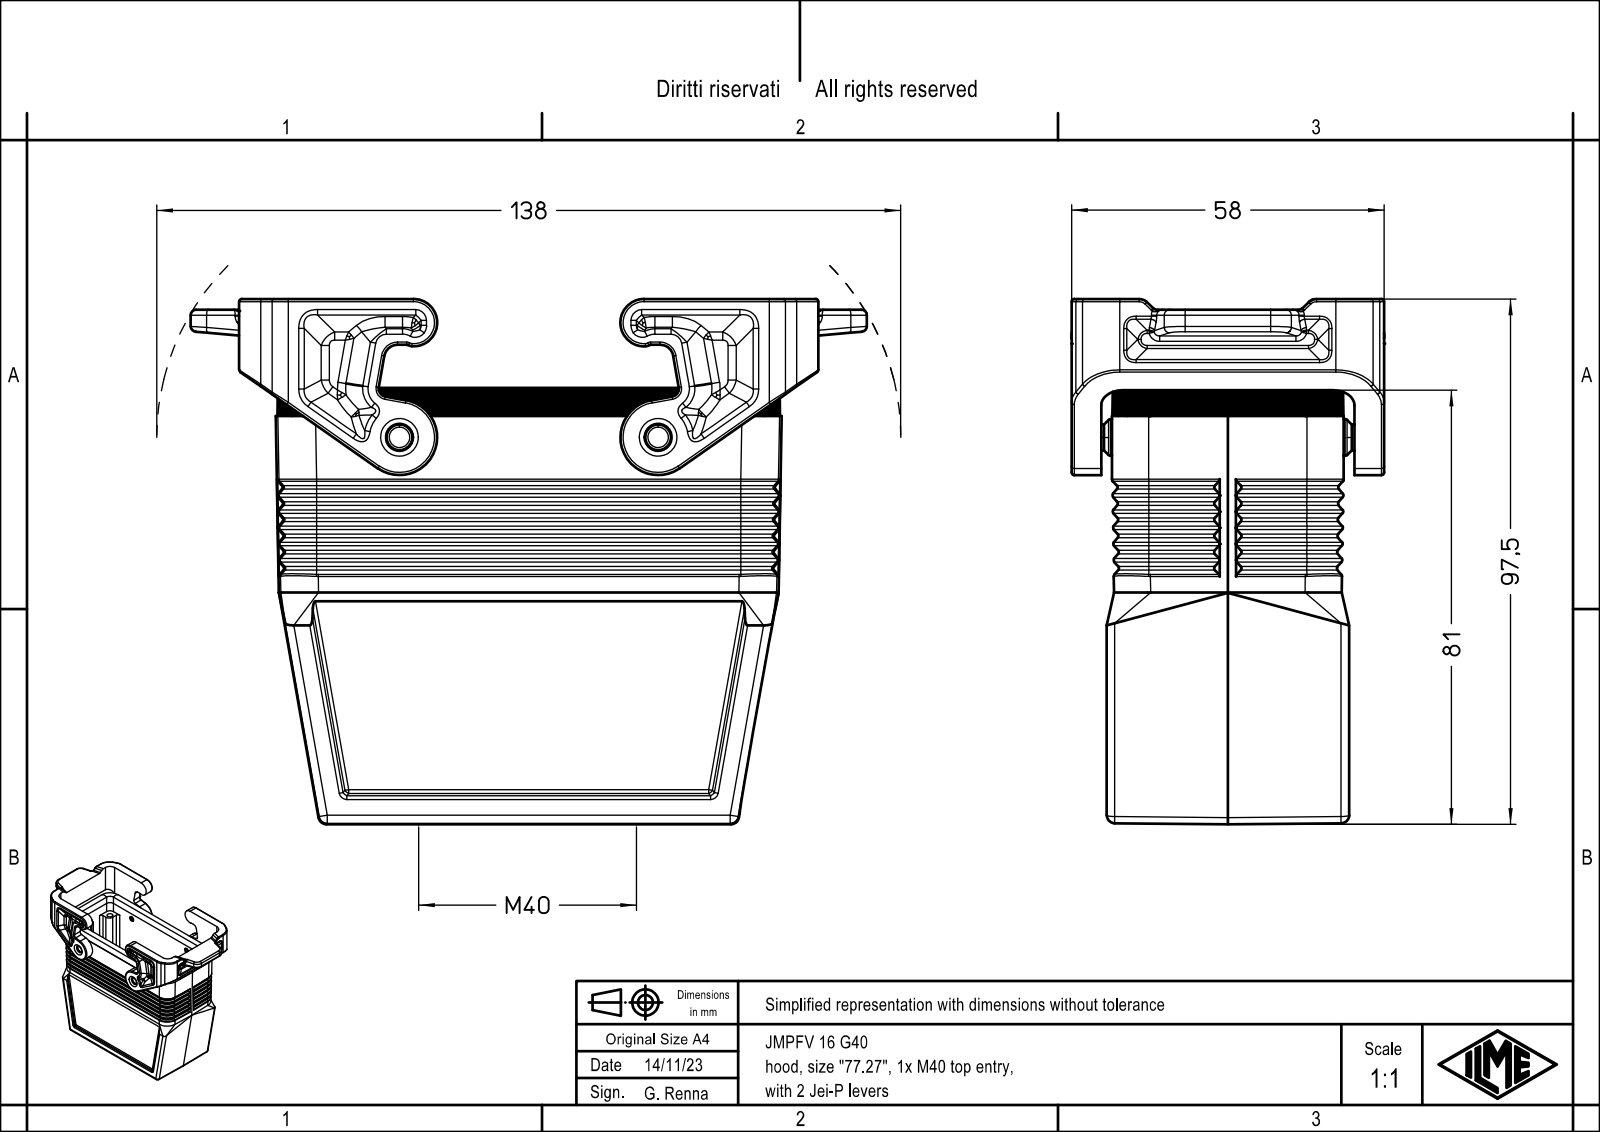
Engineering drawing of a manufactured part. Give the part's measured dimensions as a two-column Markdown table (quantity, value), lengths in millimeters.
| quantity | value |
| --- | --- |
| part name | JMPFV 16 G40 |
| STEP written by | Creo Elements/Direct Modeling 20.1B 02-Apr-2019 (C) Parametric Technology GmbH (AUTOMOTIVE_DESIGN) |
| units | millimeters |
| bodies | 1 solid, 1209 faces (334 planar, 395 cylindrical, 480 other) |
| overall size | 125.5 × 97.45 × 58.08 |
| volume | 114 023 mm³ |
| surface area | 58 543 mm² |
| round holes (diameter × count) | 3 × 4, 3.5 × 4, 4.8 × 2, 38.6 × 1 |
| round bosses / shafts (diameter × count) | 6.8 × 2 |
| partial cylindrical surfaces (radius × count) | 0.5 × 120, 1 × 48, 3 × 34, 1.5 × 26, 2 × 20, 0.33 × 15, 7 × 14, 4 × 12 |
| main face-to-face distances | 3.75, 39.25, 2, 35.5, 5.75, 43, 45, 41.25, 1, 4 |
| hole center spacings | 41.03, 27, 77.5, 82.07, 48 |
